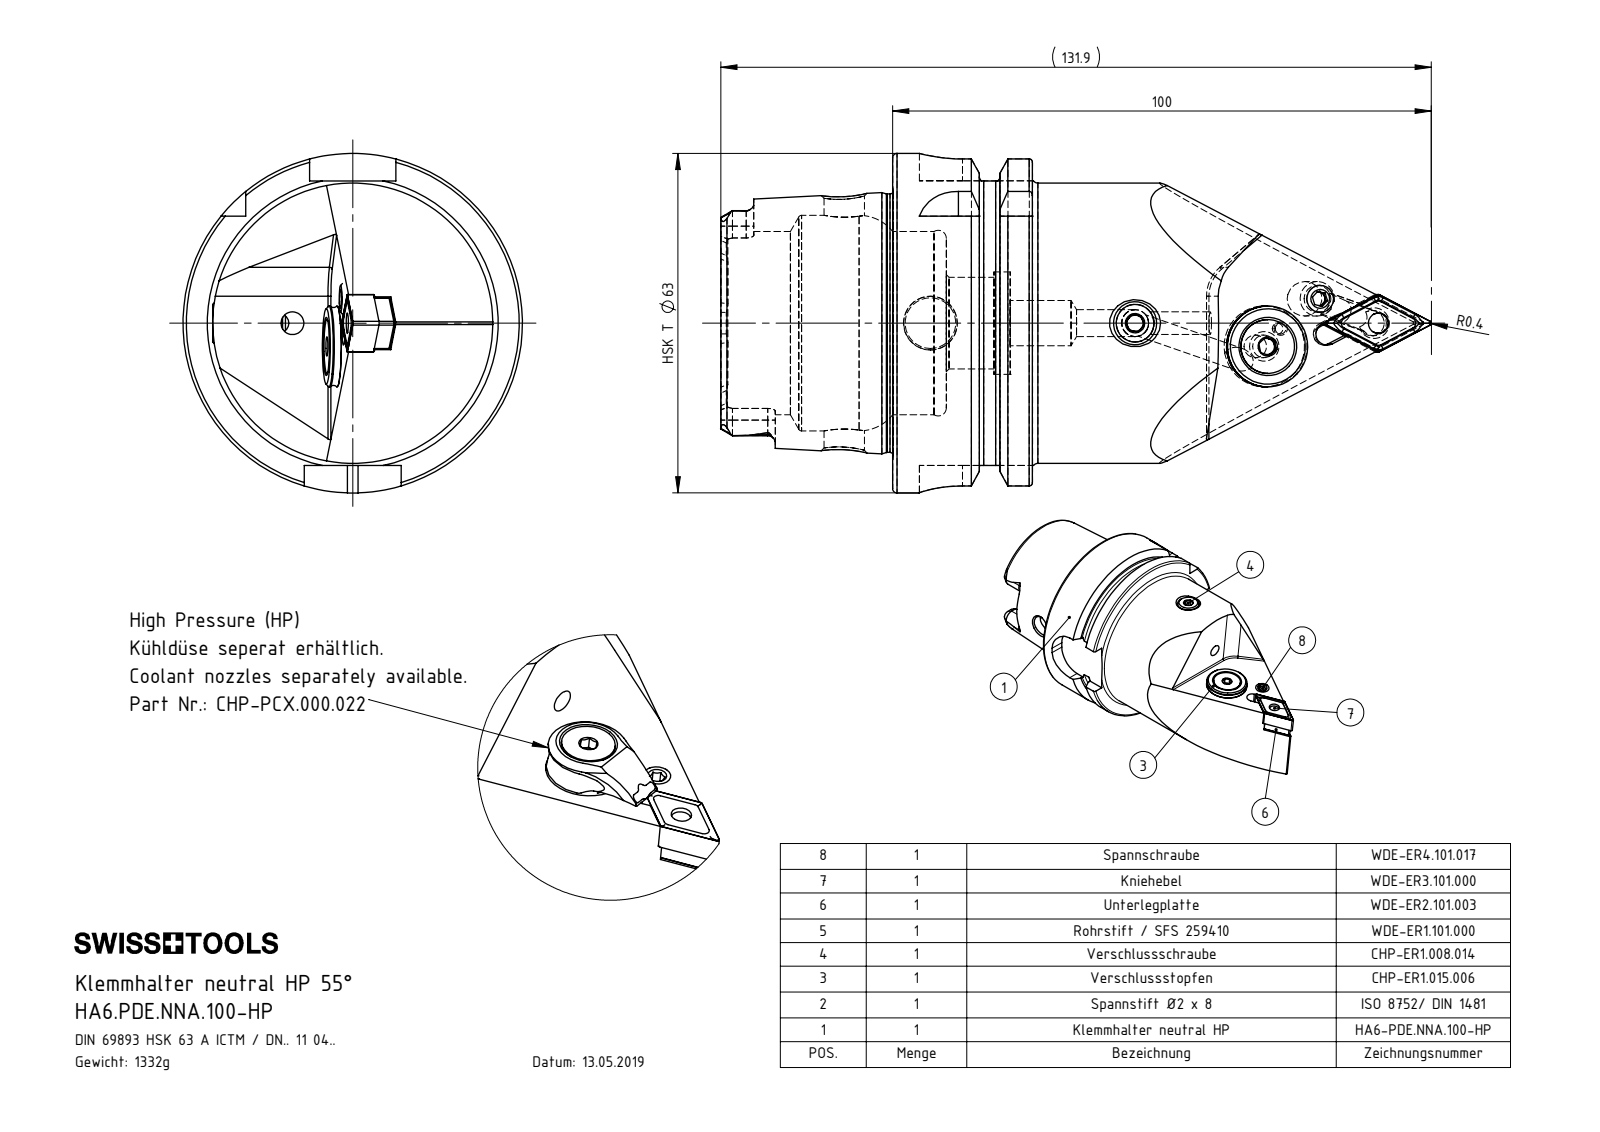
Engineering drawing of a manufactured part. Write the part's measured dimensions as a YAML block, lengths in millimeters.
part_name: "DNMG110404; DIN 7991 - M5x15; CHP-ER1.008.014_A; CHP-ER1.015.006 (+8 more)"
step_written_by: "SolidWorks 2017 (AUTOMOTIVE_DESIGN)"
units: millimeters
bodies: {solids: 11, faces: 384, planar: 173, cylindrical: 81, other: 130}
overall_size: [131.9, 63, 63]
volume: 168577
surface_area: 35983
round_holes:
  - {diameter: 4.2, count: 3}
  - {diameter: 5, count: 3}
  - {diameter: 2.5, count: 2}
  - {diameter: 1.2, count: 1}
  - {diameter: 2, count: 1}
  - {diameter: 3, count: 1}
  - {diameter: 3.81, count: 1}
  - {diameter: 4.8, count: 1}
  - {diameter: 5.2, count: 1}
  - {diameter: 6.4, count: 1}
  - {diameter: 7, count: 1}
  - {diameter: 7.5, count: 1}
round_bosses_or_shafts:
  - {diameter: 63, count: 1}
  - {diameter: 54.95, count: 1}
  - {diameter: 52, count: 1}
  - {diameter: 47.94, count: 1}
  - {diameter: 15, count: 1}
  - {diameter: 13.4, count: 1}
  - {diameter: 10, count: 1}
  - {diameter: 8, count: 1}
partial_cylinders:
  - {radius: 0.4, count: 8}
  - {radius: 1.4, count: 6}
  - {radius: 2.1, count: 4}
  - {radius: 2.88, count: 4}
  - {radius: 8, count: 4}
  - {radius: 0.5, count: 2}
  - {radius: 1.83, count: 1}
  - {radius: 1.85, count: 1}
face_to_face_distances: [25.95, 16, 9.95, 31.9, 41.85, 57.85, 52.8, 21.8, 11.85, 4.51]
hole_center_spacings: [4.5, 4.51, 4.52, 4.53, 8.79, 8.81, 8.82, 8.84]
